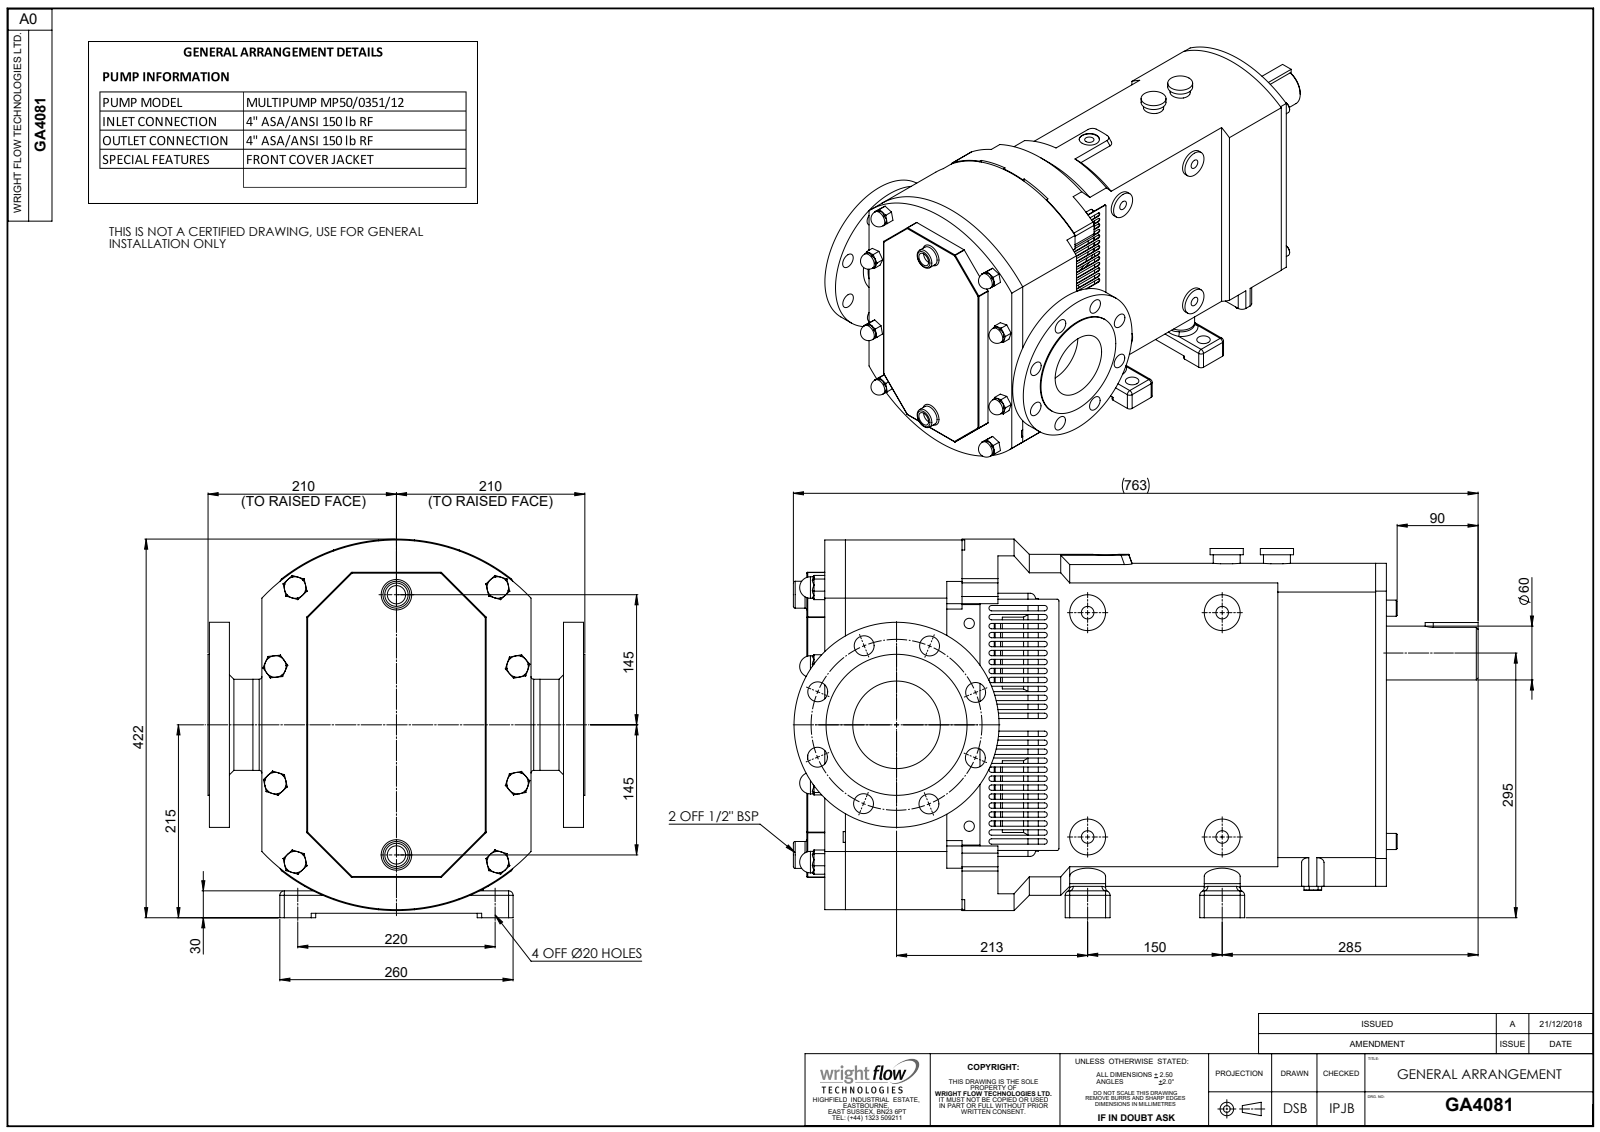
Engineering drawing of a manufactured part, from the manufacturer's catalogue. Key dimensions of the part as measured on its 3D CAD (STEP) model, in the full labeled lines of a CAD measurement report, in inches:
Part name (STEP PRODUCT): GA4081; Copy of CP50S-0351 H TSD^GA4081; Copy of Z94-5301-66 - 4 INCH ASA 150^GA4081; Copy of MP50 Jacket Front Cover^GA4081
STEP written by: SolidWorks 2023 (AUTOMOTIVE_DESIGN)
Units: inches
Bodies: 4 solids, 1223 faces (507 planar, 438 cylindrical, 278 other)
Overall size (bounding box): 30.049 × 16.614 × 16.535
Volume: 2 932 in³ · Surface area: 2 575 in²
Round holes (diameter × count): ⌀0.874 ×16, ⌀0.551 ×4, ⌀0.787 ×4, ⌀0.453 ×2, ⌀0.803 ×2, ⌀1.378 ×2, ⌀0.545 ×1, ⌀1.181 ×1, ⌀3.843 ×1
Round bosses / shafts (diameter × count): ⌀1.575 ×8, ⌀0.945 ×8, ⌀1.181 ×4, ⌀0.709 ×4, ⌀6.654 ×2, ⌀3.15 ×2, ⌀2.756 ×2, ⌀2.677 ×2
Partial cylindrical surfaces — rounded edges, fillets, slot ends (radius × count): R0.118 ×52, R0.197 ×36, R0.039 ×16, R0.236 ×14, R0.315 ×12, R0.079 ×4, R0.354 ×1, R6.083 ×1
Main face-to-face distances: 6.772, 6.142, 0.787, 7.421, 0.65, 24.646, 25.433, 1.87, 2.52, 9.291
Hole centre spacings: 2.87, 3.75, 5.303, 6.929, 7.5, 0.03, 2.843, 2.898
